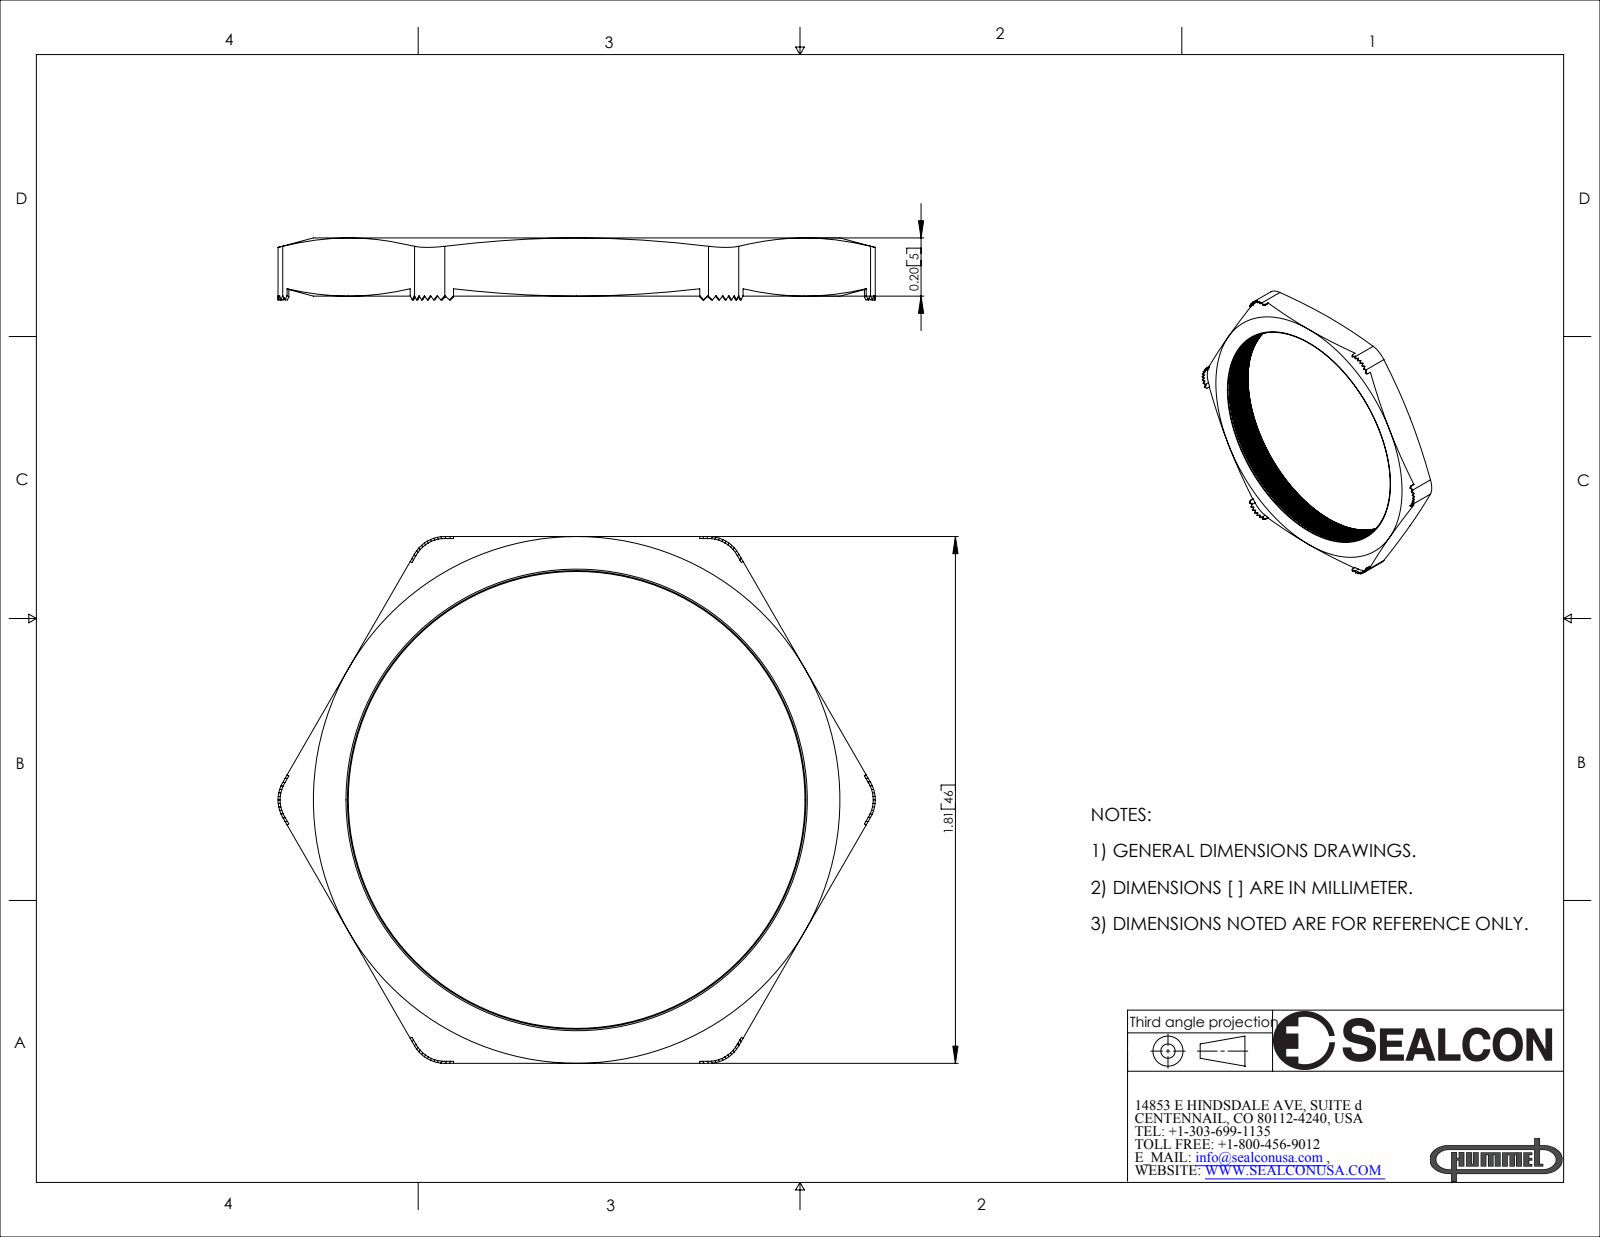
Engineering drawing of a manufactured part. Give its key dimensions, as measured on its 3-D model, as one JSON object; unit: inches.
{"part_name": "NM-40-BE", "step_written_by": "SolidWorks 2007 (CONFIG_CONTROL_DESIGN)", "units": "inches", "bodies": {"solids": 1, "faces": 248, "planar": 116, "cylindrical": 46, "other": 86}, "overall_size": [2.053, 1.81, 0.213], "volume_in3": 0.169, "surface_area_in2": 4.864, "round_holes": [[1.57, 1]], "partial_cylinders_radius": [[0.113, 6], [0.12, 6]], "face_to_face_distances": [0.2, 1.81, 1.803, 1.796, 0.019, 0.094, 0.037, 0.076, 0.037, 0.056]}
